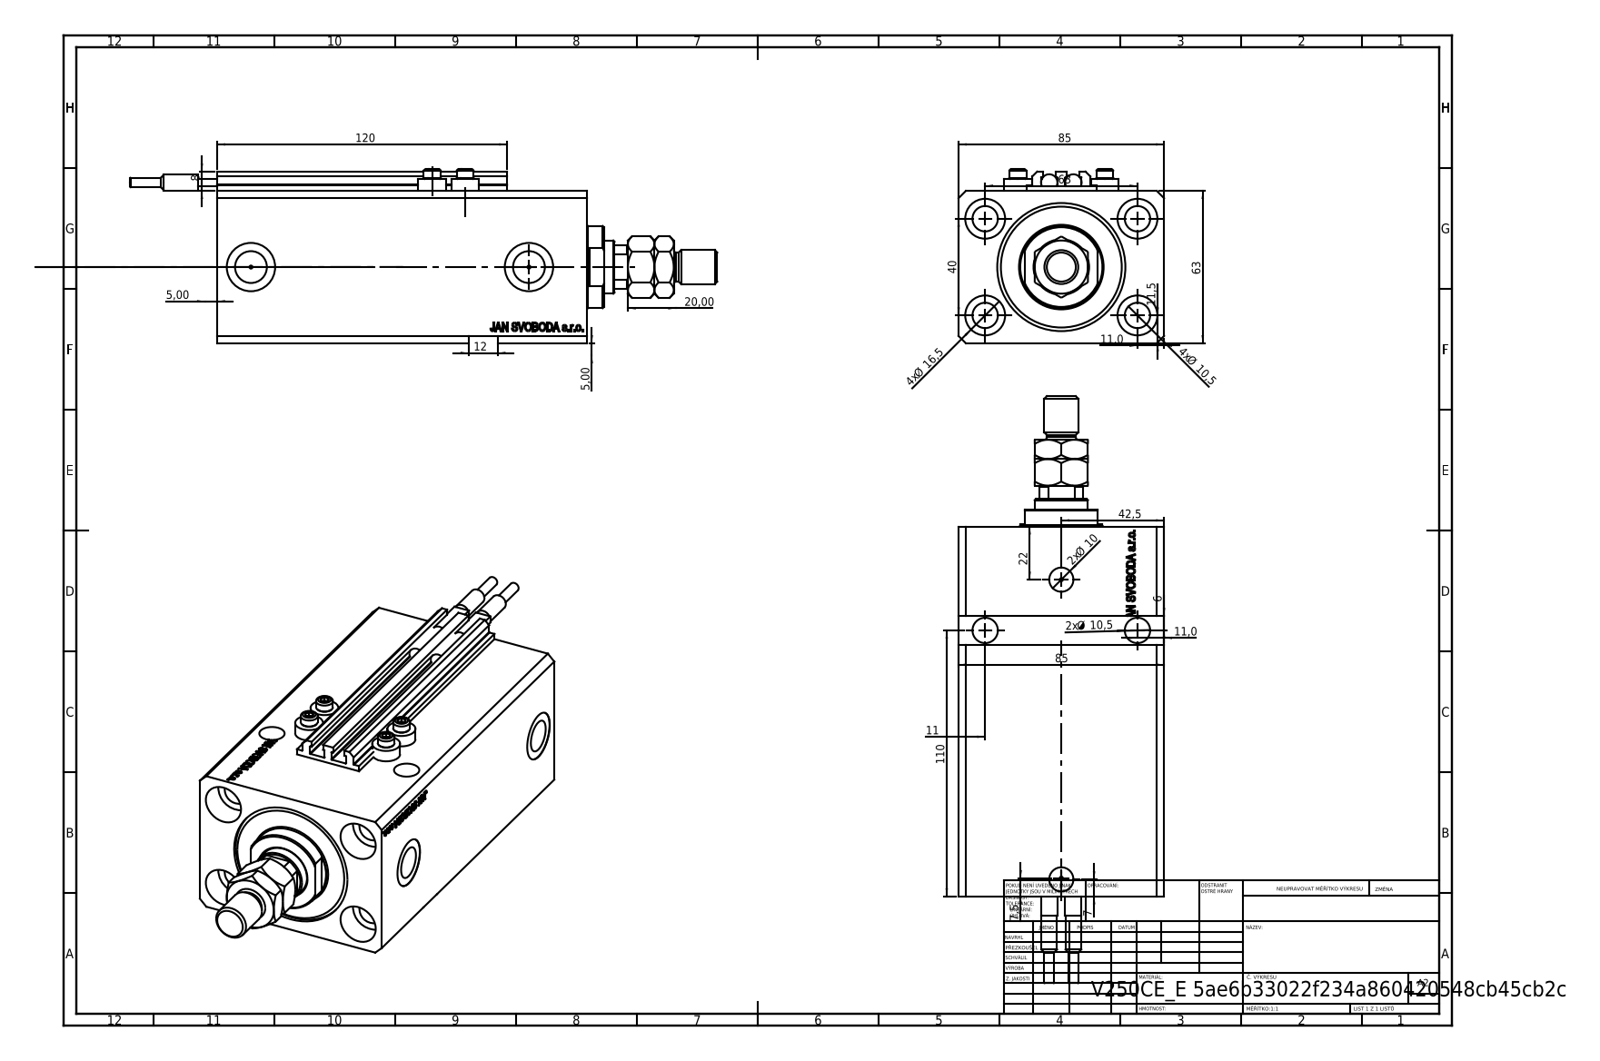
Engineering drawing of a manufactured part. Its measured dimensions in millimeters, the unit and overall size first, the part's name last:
Units: millimetres
Overall size (bounding box): 242.9 × 85 × 72
Round holes (diameter × count): ⌀10.5 ×6, ⌀1.25 ×4, ⌀4 ×4, ⌀16.5 ×4, ⌀10 ×2, ⌀13.16 ×2, ⌀20 ×2, ⌀12.5 ×1, ⌀22 ×1, ⌀40 ×1, ⌀53 ×1
Round bosses / shafts (diameter × count): ⌀11.6 ×4, ⌀7 ×4, ⌀6.8 ×2, ⌀6.5 ×2, ⌀4 ×2, ⌀34 ×1, ⌀14 ×1, ⌀12 ×1
Partial cylindrical surfaces — rounded edges, fillets, slot ends (radius × count): R0.2 ×10, R10.5 ×1
Main face-to-face distances: 63, 85, 153, 125.9, 27.1, 65, 11.4, 114.5, 141.6, 3
Hole centre spacings: 37.31, 63, 13.6, 15.4, 24.96, 33.62, 36, 37.86
Volume: 702 148 mm³ · Surface area: 147 862 mm²
Bodies: 11 solids, 1204 faces (586 planar, 154 cylindrical, 464 other)
Part name (STEP PRODUCT): V250CE_E_Body; SWITCH_V250CE; V250CE_C_VCP; V250CE_VC_E (+2 more)
STEP written by: SolidWorks 2019 (CONFIG_CONTROL_DESIGN)
